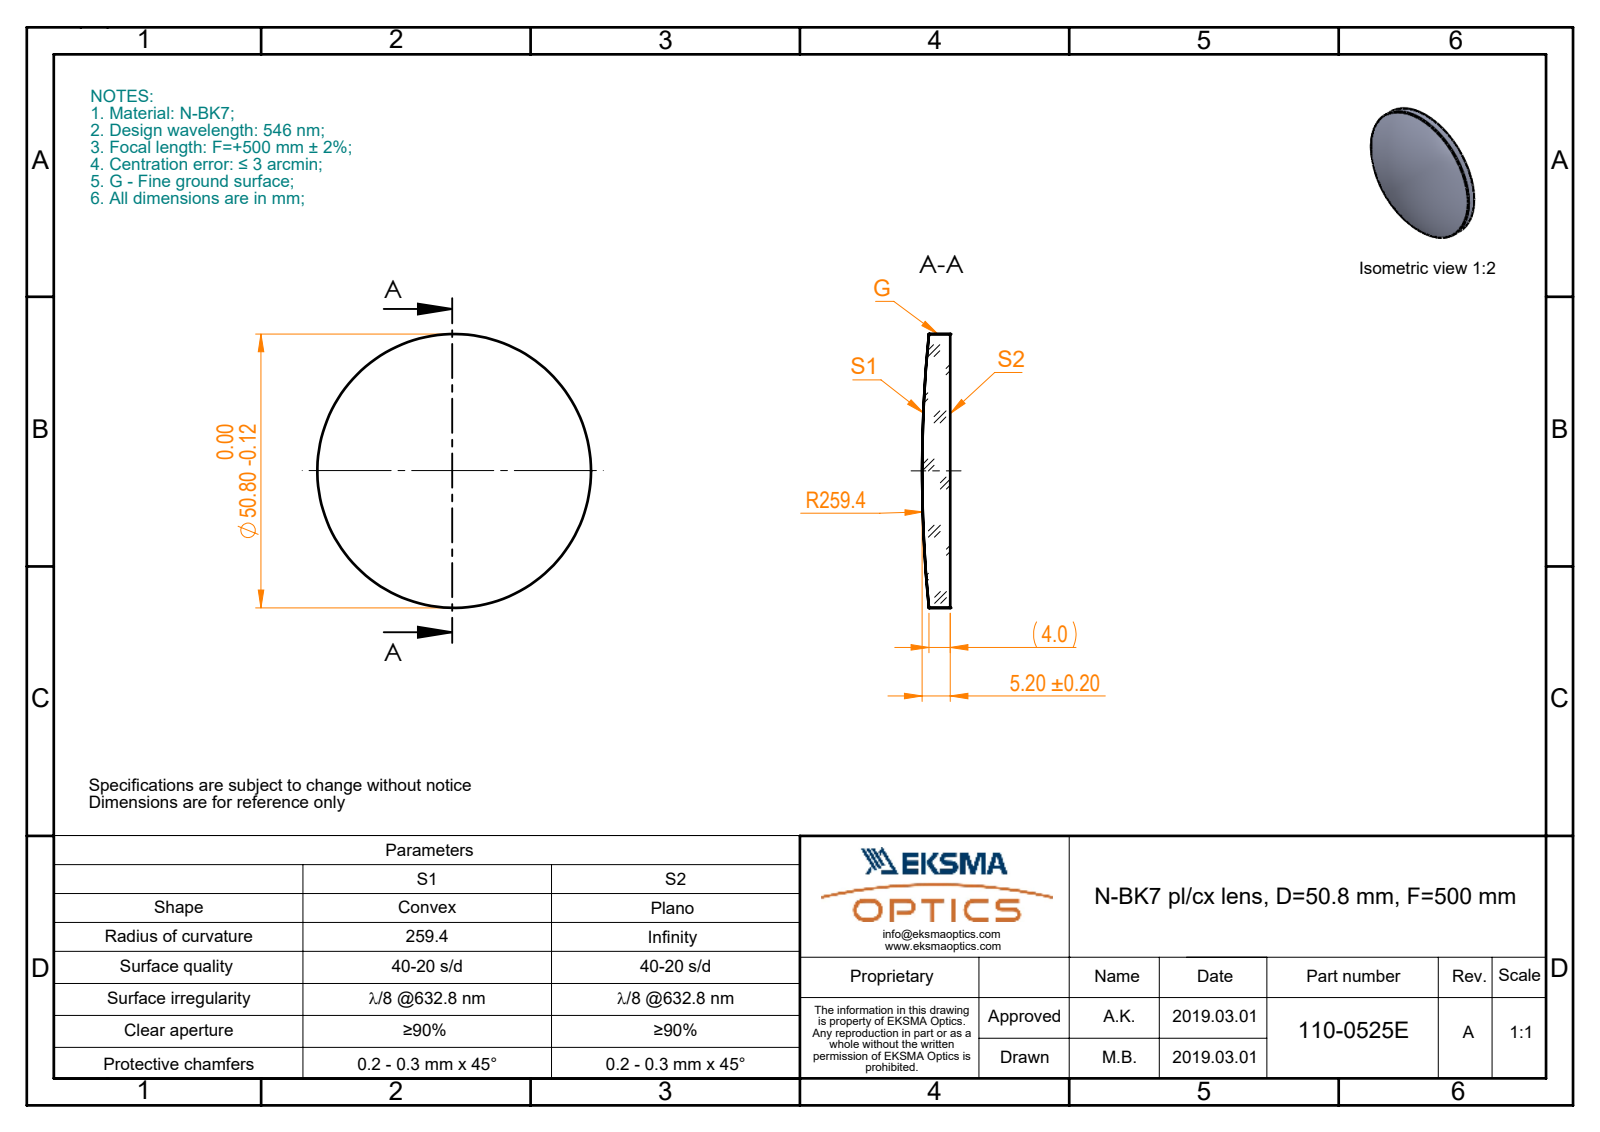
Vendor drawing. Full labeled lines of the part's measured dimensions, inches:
Part name (STEP PRODUCT): 110-0525E BK7 pl-cx 50.8 F500
STEP written by: SolidWorks 2017 (CONFIG_CONTROL_DESIGN)
Units: inches
Bodies: 1 solid, 5 faces (1 planar, 2 cylindrical, 2 other)
Overall size (bounding box): 2 × 2 × 0.205
Volume: 0.566 in³ · Surface area: 7.268 in²
Round bosses / shafts (diameter × count): ⌀2 ×1
